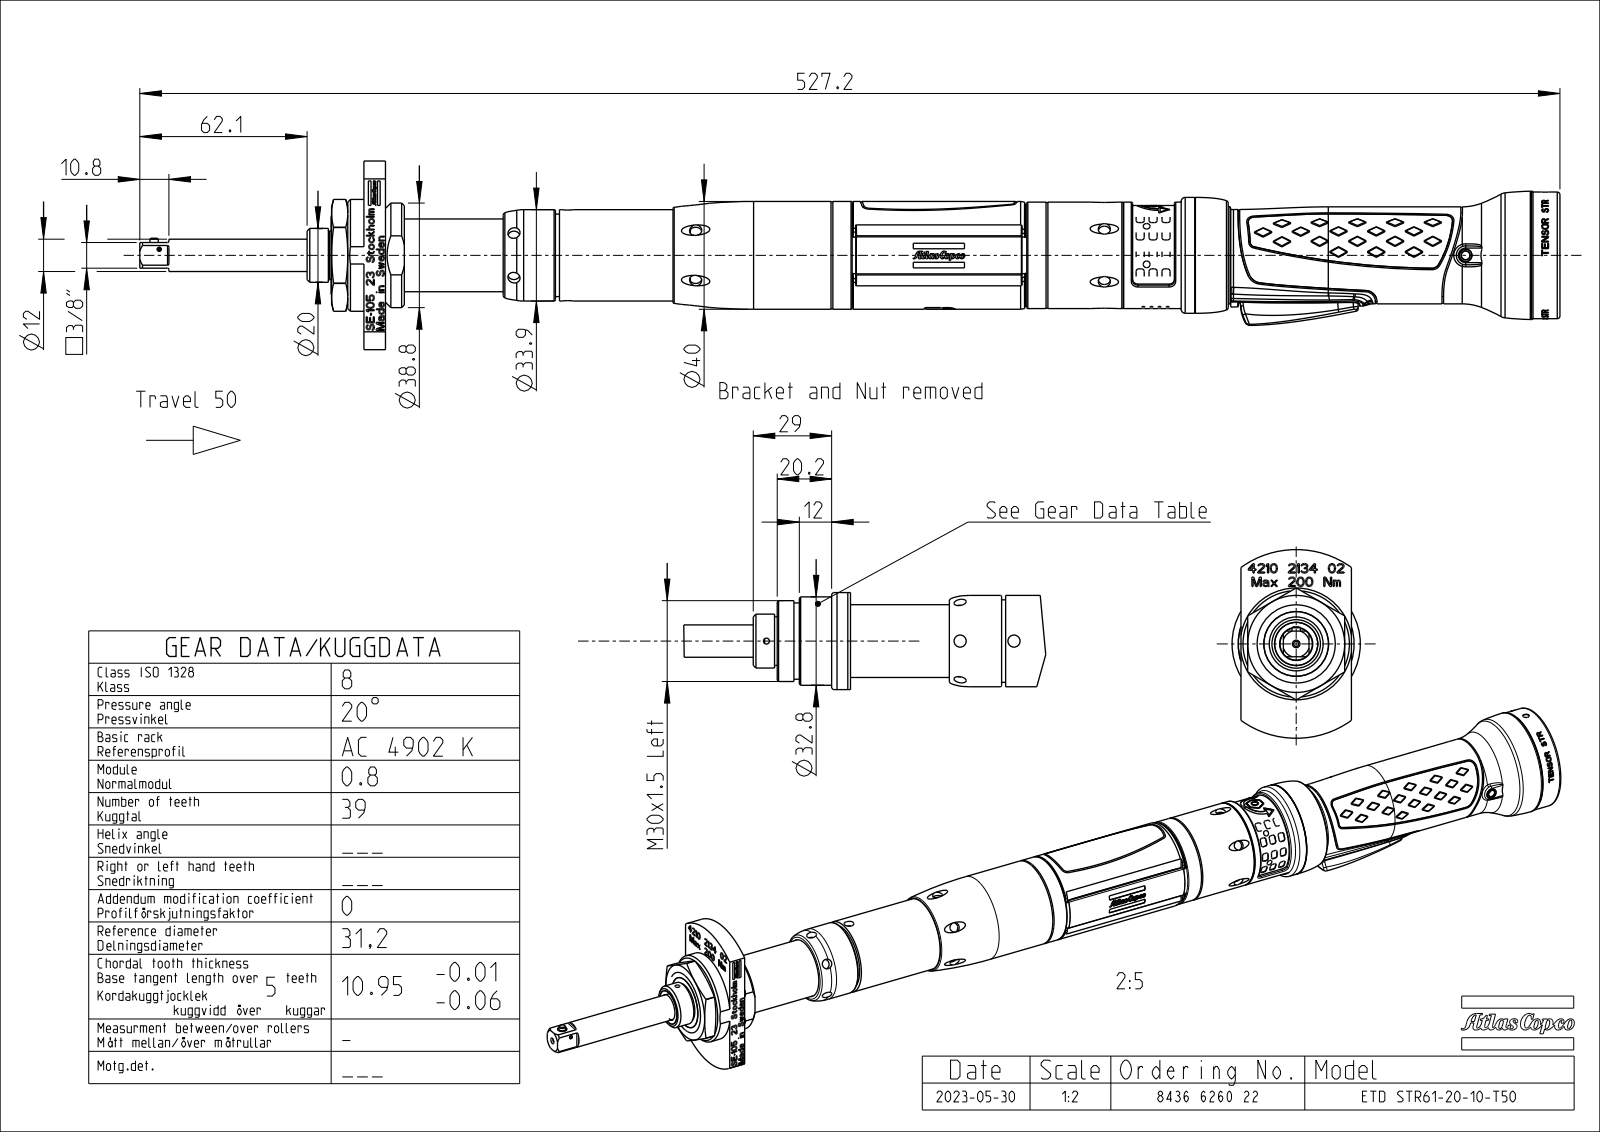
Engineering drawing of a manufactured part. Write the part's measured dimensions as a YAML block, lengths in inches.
part_name: "EXTTTT_COMPPP_SW0001"
step_written_by: "CREO PARAMETRIC BY PTC INC, 2022414 (CONFIG_CONTROL_DESIGN)"
units: inches
bodies: {solids: 2, faces: 4191, planar: 1806, cylindrical: 644, other: 1741}
overall_size: [20.757, 2.756, 1.875]
volume: 31.88
surface_area: 129.2
round_holes:
  - {diameter: 0.039, count: 12}
  - {diameter: 0.177, count: 10}
  - {diameter: 0.063, count: 2}
  - {diameter: 0.015, count: 1}
  - {diameter: 0.059, count: 1}
  - {diameter: 0.075, count: 1}
  - {diameter: 0.118, count: 1}
  - {diameter: 0.126, count: 1}
  - {diameter: 0.185, count: 1}
  - {diameter: 0.197, count: 1}
  - {diameter: 0.472, count: 1}
  - {diameter: 1.461, count: 1}
round_bosses_or_shafts:
  - {diameter: 1.85, count: 1}
  - {diameter: 1.693, count: 1}
  - {diameter: 1.634, count: 1}
  - {diameter: 1.575, count: 1}
  - {diameter: 1.555, count: 1}
  - {diameter: 1.457, count: 1}
  - {diameter: 1.449, count: 1}
  - {diameter: 1.417, count: 1}
partial_cylinders:
  - {radius: 0.008, count: 58}
  - {radius: 0.012, count: 44}
  - {radius: 0.02, count: 43}
  - {radius: 0.079, count: 14}
  - {radius: 0.118, count: 12}
  - {radius: 0.024, count: 4}
  - {radius: 0.031, count: 4}
  - {radius: 0.011, count: 3}
face_to_face_distances: [0.02, 17.166, 0.315, 17.481, 1.329, 0.276, 1.614, 16.891, 0.591, 1.516]
hole_center_spacings: [0.118, 0.236, 0.354, 2.656, 5.974, 8.629, 0.196, 0.2]
